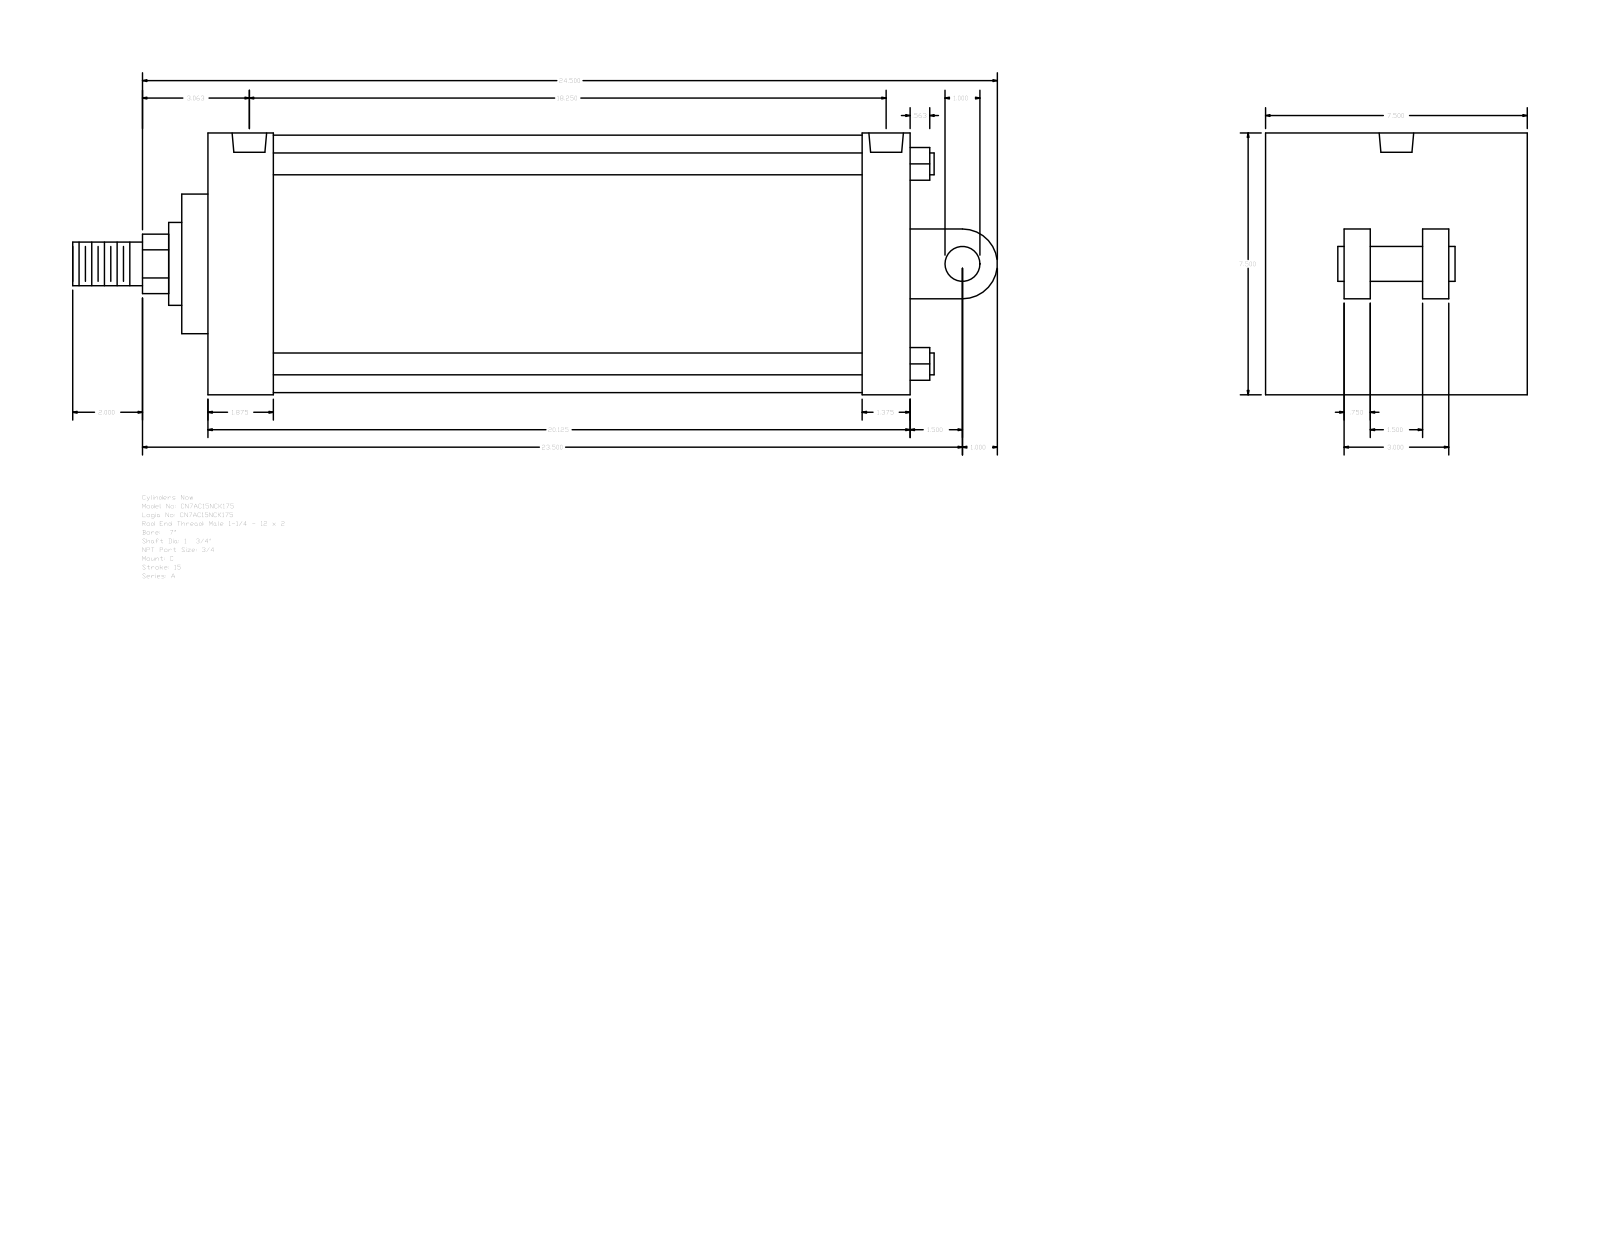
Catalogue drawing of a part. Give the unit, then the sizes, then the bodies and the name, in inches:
Units: inches
Overall size (bounding box): 26.5 × 7.5 × 7.5
Round holes (diameter × count): ⌀0.594 ×4, ⌀0.989 ×2
Round bosses / shafts (diameter × count): ⌀0.625 ×4, ⌀7.375 ×1, ⌀2.375 ×1, ⌀1.75 ×1, ⌀1.25 ×1, ⌀1 ×1
Partial cylindrical surfaces — rounded edges, fillets, slot ends (radius × count): R0.852 ×1, R1 ×1
Main face-to-face distances: 7.5, 20.125, 0.75, 3, 2.25, 5.75, 1.75, 2.75, 1.875, 18.25
Hole centre spacings: 0.219, 17.812, 18.031, 18.25
Bodies: 0 solids, 104 faces (75 planar, 29 cylindrical, 0 other)
Part name (STEP PRODUCT): A_C__0700_1.75
STEP written by: GSSL Pune (CONFIG_CONTROL_DESIGN)
